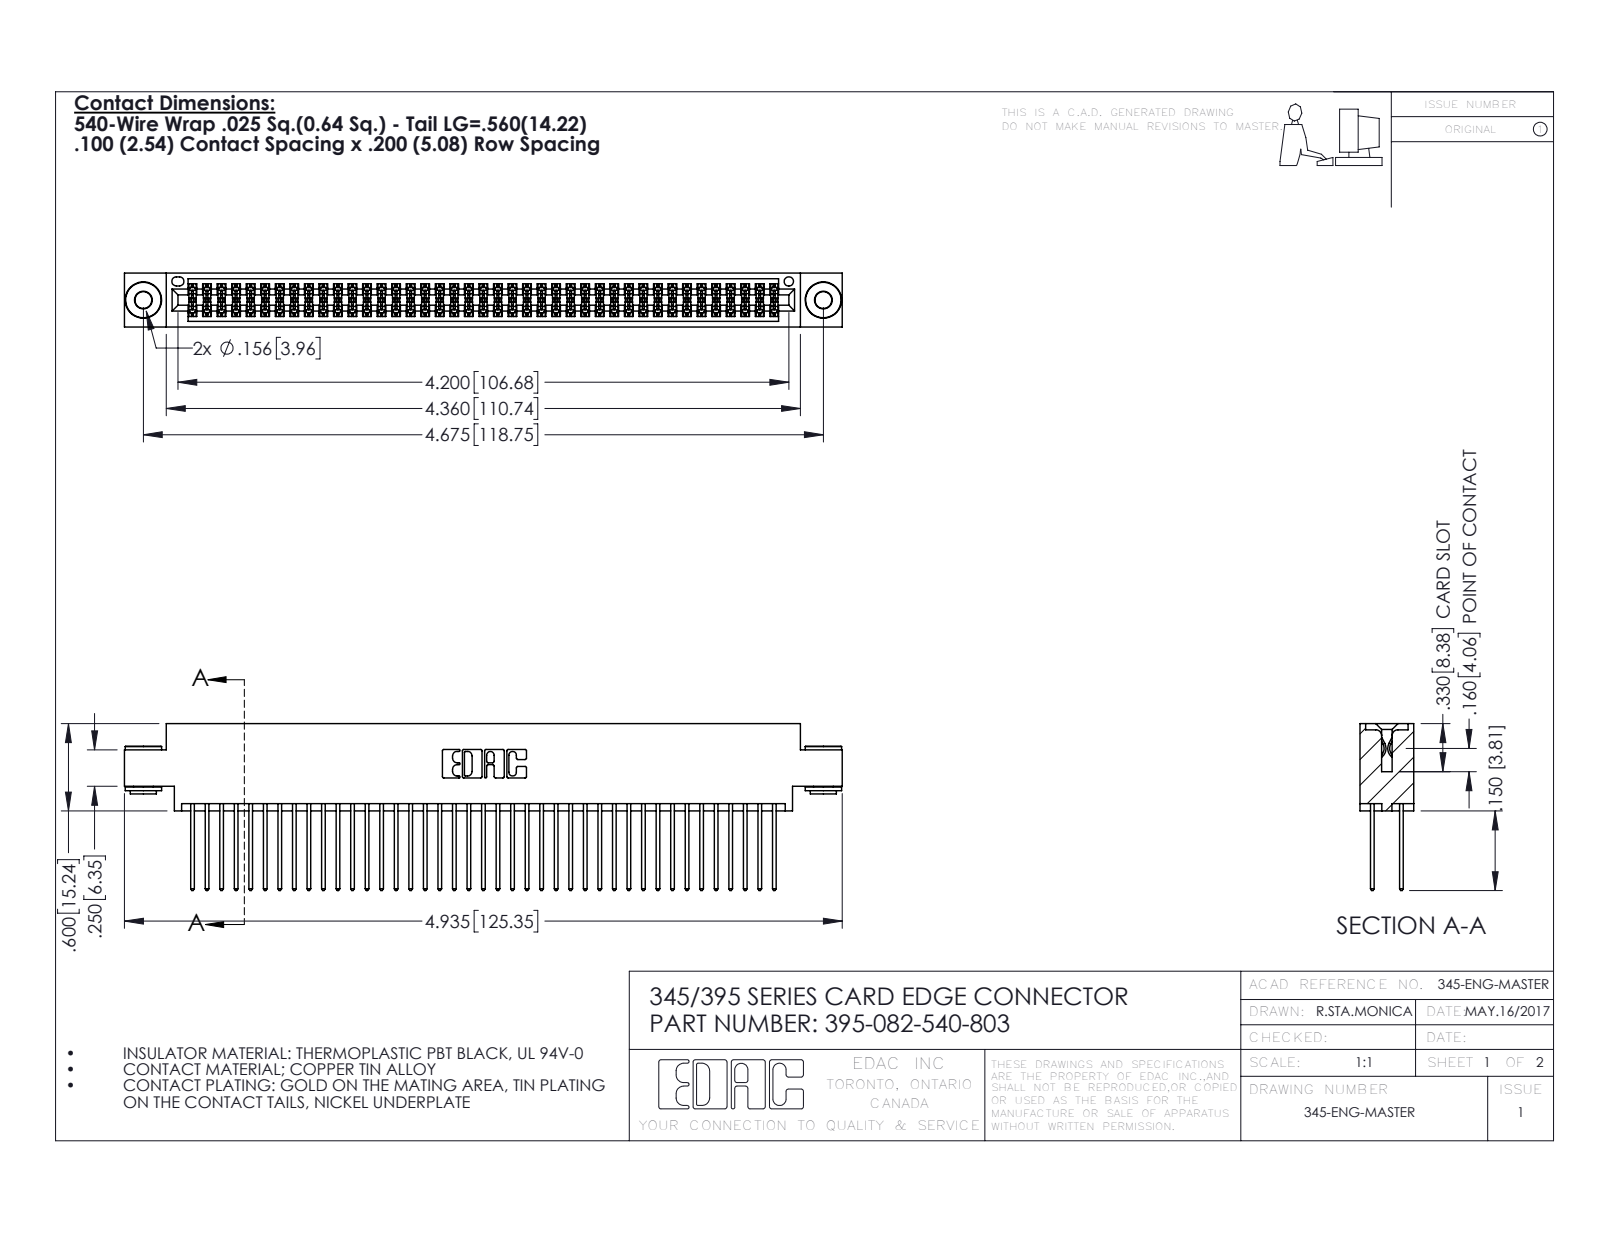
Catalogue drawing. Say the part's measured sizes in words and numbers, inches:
The part is named "345-292-001_345-293-140; 345 Part_0.170 Offset - 0.156 Dia-TH; 395-082-540-803; 345-250-002_345-250-002-102". Its 3-D file was written by "SolidWorks 2016 (CONFIG_CONTROL_DESIGN)". It is 85 solids with 4268 faces: 2800 planar, 1460 cylindrical and 8 other. Overall it measures 4.935 by 1.147 by 0.37 inches. Its volume is 0.756 cubic inches and its surface area 31.12 square inches. Round holes: 2 of diameter 0.116, 2 of diameter 0.156, 1 of diameter 0.064. Round bosses or shafts: 2 of diameter 0.25, 2 of diameter 0.18, 2 of diameter 0.136. Partial cylindrical surfaces (rounded edges, fillets, slot ends): 123 of radius 0.006, 82 of radius 0.01, 22 of radius 0.01, 6 of radius 0.007, 6 of radius 0.031, 3 of radius 0.026, 2 of radius 0.014, 2 of radius 0.019. The main face-to-face distances are 0.072, 0.298, 0.2, 0.098, 0.272, 0.025, 0.37, 0.225, 0.175, 0.149. The hole center spacings are 0.27, 4.439, 4.675.
